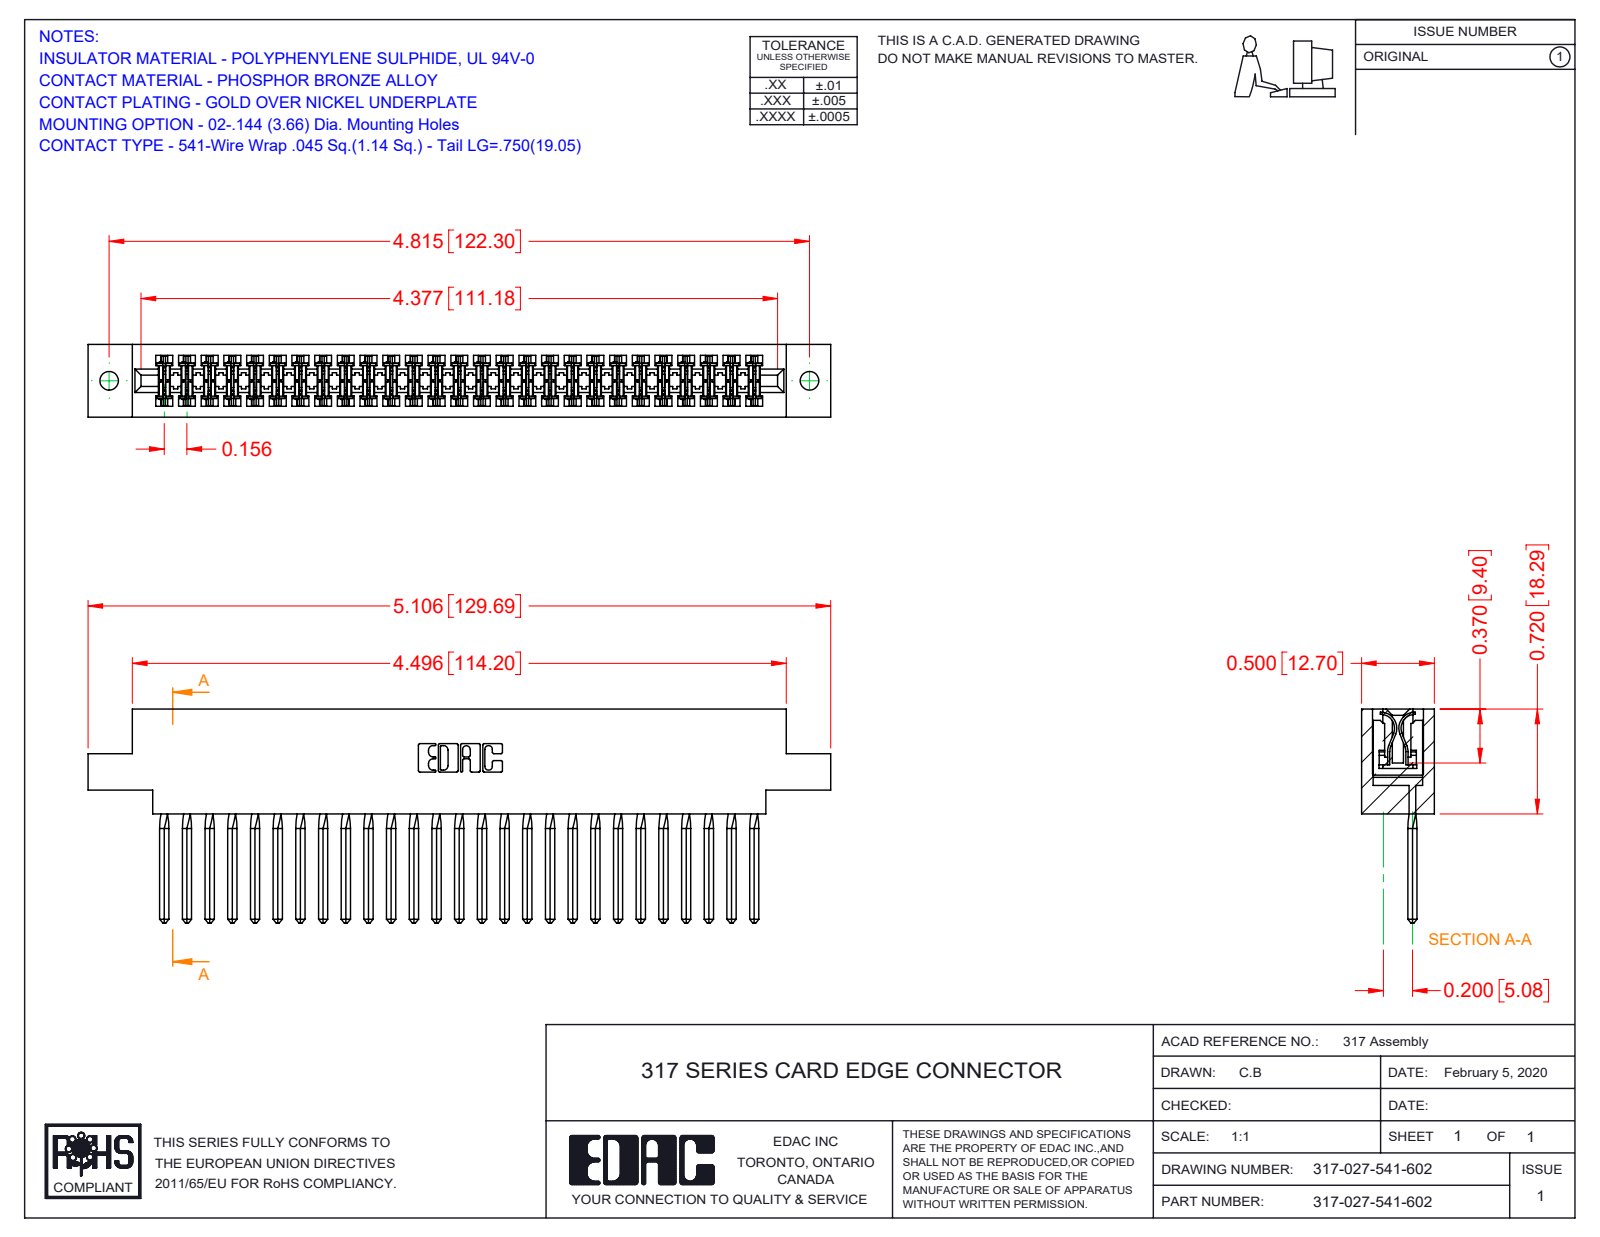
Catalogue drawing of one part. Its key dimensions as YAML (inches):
part_name: "317-290-002_541; 317-027-541-602; 317 Part_.144 Dia"
step_written_by: "SolidWorks 2016 (CONFIG_CONTROL_DESIGN)"
units: inches
bodies: {solids: 28, faces: 4206, planar: 3406, cylindrical: 692, other: 108}
overall_size: [5.106, 1.47, 0.5]
volume: 1.253
surface_area: 43.79
round_holes:
  - {diameter: 0.128, count: 2}
partial_cylinders:
  - {radius: 0.015, count: 54}
  - {radius: 0.01, count: 22}
  - {radius: 0.007, count: 6}
  - {radius: 0.031, count: 6}
  - {radius: 0.026, count: 3}
  - {radius: 0.095, count: 2}
  - {radius: 0.1, count: 2}
  - {radius: 0.11, count: 2}
face_to_face_distances: [0.5, 0.075, 0.425, 0.35, 0.11, 0.195, 0.72, 0.115, 0.211, 0.289]
hole_center_spacings: [4.815]
